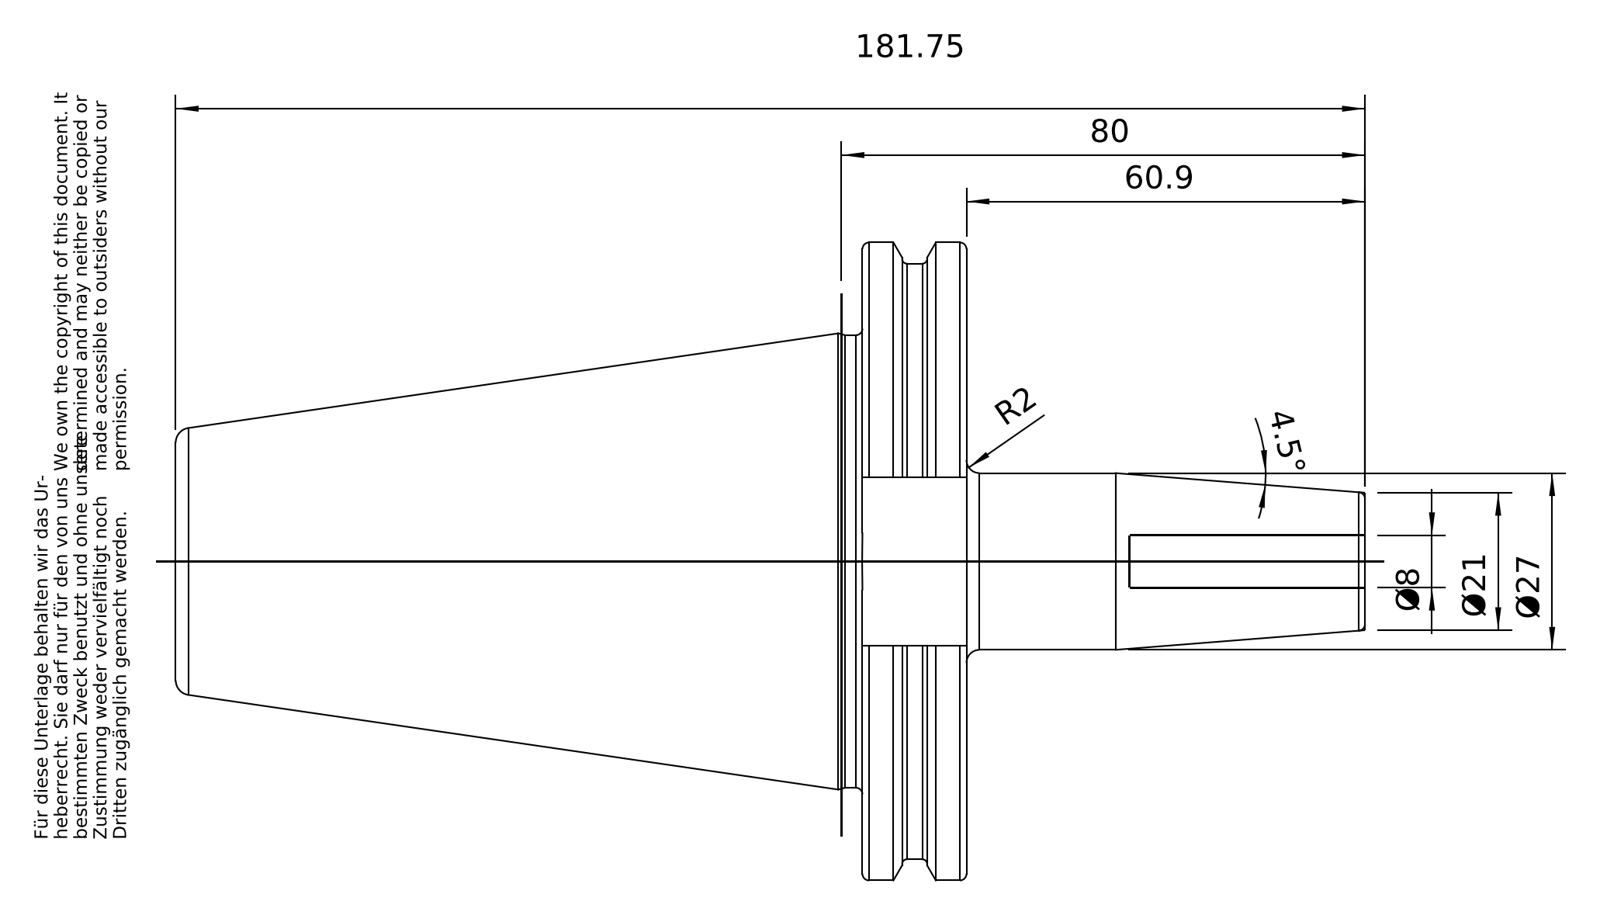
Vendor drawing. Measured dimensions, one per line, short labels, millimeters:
name: 50-440-08
written by: PRO/ENGINEER BY PARAMETRIC TECHNOLOGY CORPORATION, 2010430 (CONFIG_CONTROL_DESIGN)
unit: mm
bodies: 1 solid, 93 faces (21 planar, 24 cylindrical, 48 other)
size: 181.6 × 97.47 × 94
volume: 367 995 mm³; area: 48 045 mm²
holes: 1× ⌀8, 1× ⌀20.75, 1× ⌀25.01, 1× ⌀25.7
bosses: 1× ⌀91, 1× ⌀69.15, 1× ⌀27, 1× ⌀24.01
rounds: 1× R1.75, 1× R48.74
face distances: 15.85, 72.8, 104.8, 120.65, 25.8, 181.6, 76.8, 60.95, 48, 56.8
